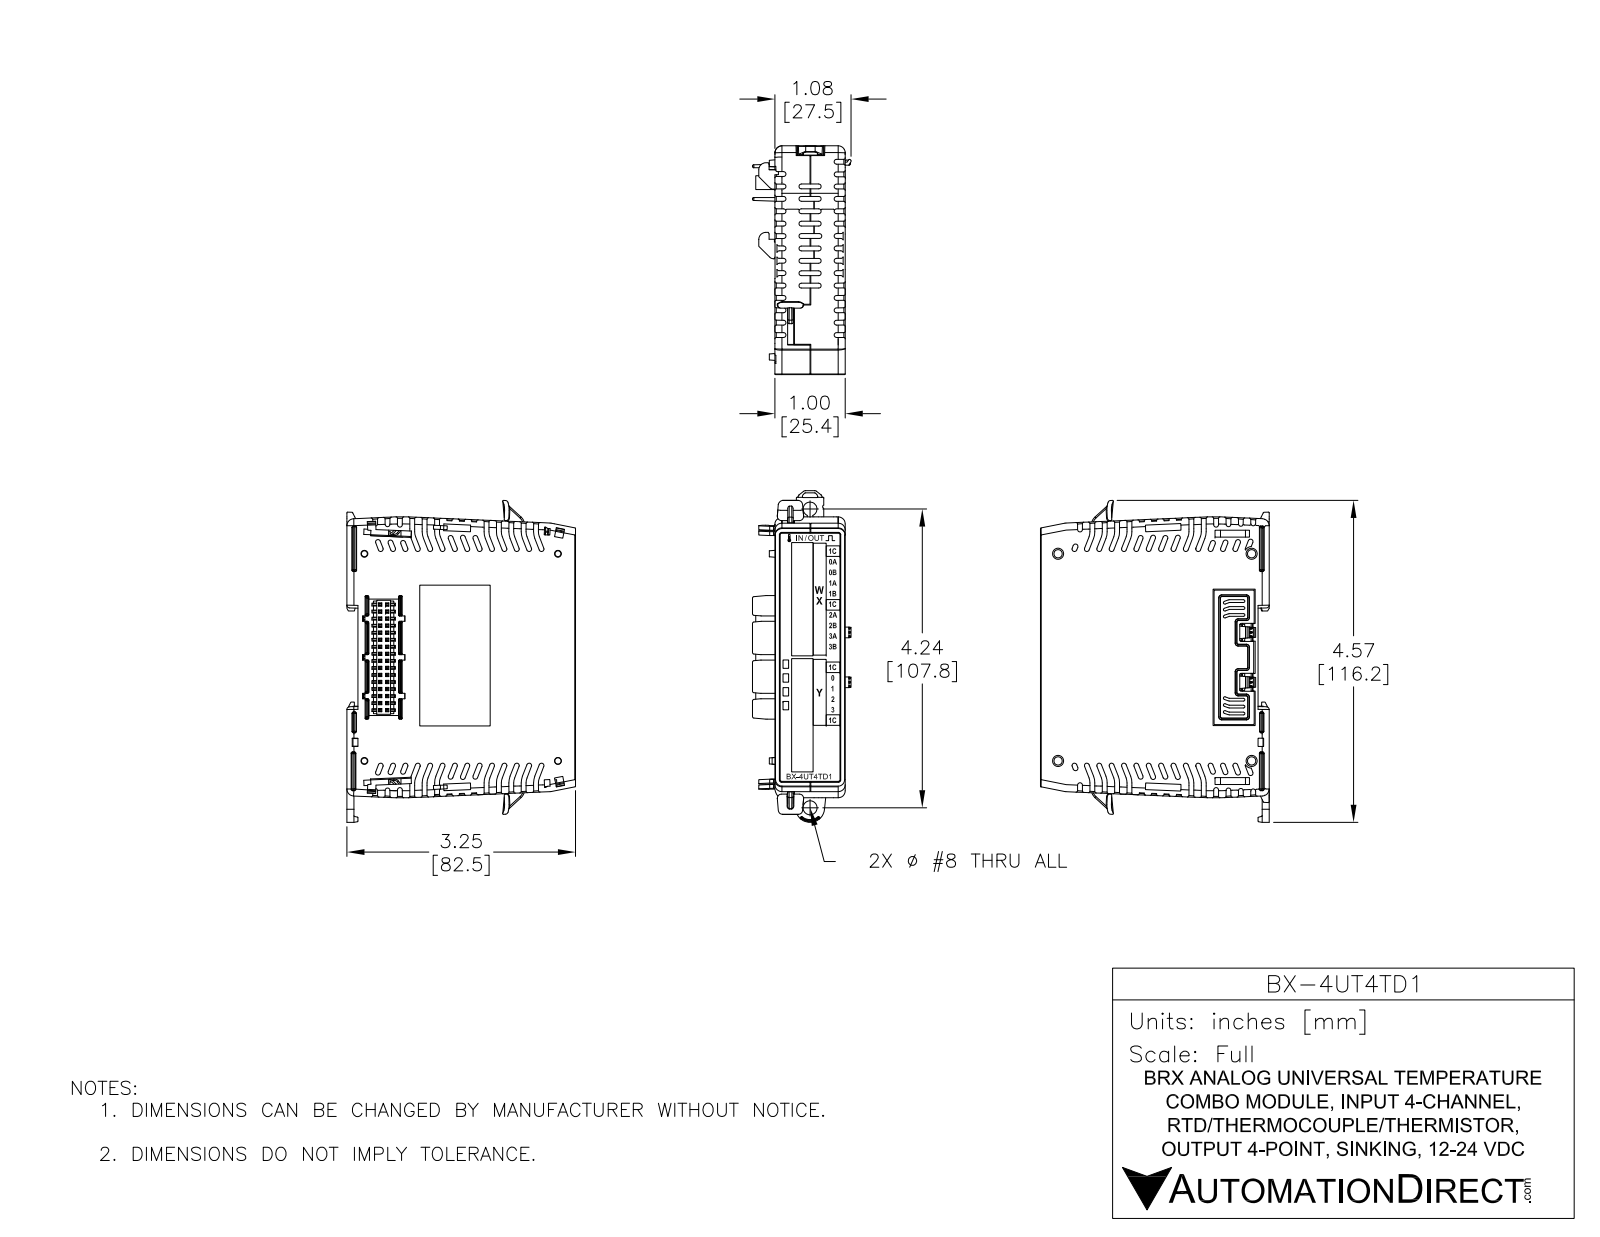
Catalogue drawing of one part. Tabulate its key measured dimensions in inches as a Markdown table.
| quantity | value |
| --- | --- |
| part name | BX-4UT4TD1 |
| STEP written by | SolidWorks 2017 (AUTOMOTIVE_DESIGN) |
| units | inches |
| bodies | 16 solids, 4175 faces (2932 planar, 672 cylindrical, 571 other) |
| overall size | 4.586 × 3.25 × 1.402 |
| volume | 11.58 in³ |
| surface area | 72.51 in² |
| round holes (diameter × count) | 0.047 × 2, 0.065 × 2, 0.118 × 2, 0.118 × 2, 0.04 × 1, 0.199 × 1 |
| round bosses / shafts (diameter × count) | 0.062 × 2, 0.059 × 2, 0.044 × 1, 0.036 × 1 |
| partial cylindrical surfaces (radius × count) | 0.005 × 102, 0.008 × 101, 0.01 × 47, 0.02 × 34, 0.005 × 24, 0.062 × 20, 0.117 × 14, 0.039 × 13 |
| main face-to-face distances | 1, 3.211, 3.22, 0.475, 0.039, 0.157, 3.053, 3.063, 0.078, 0.1 |
| hole center spacings | 0.1, 0.824, 0.919, 1.3, 2.093, 2.193, 2.585, 2.617 |
